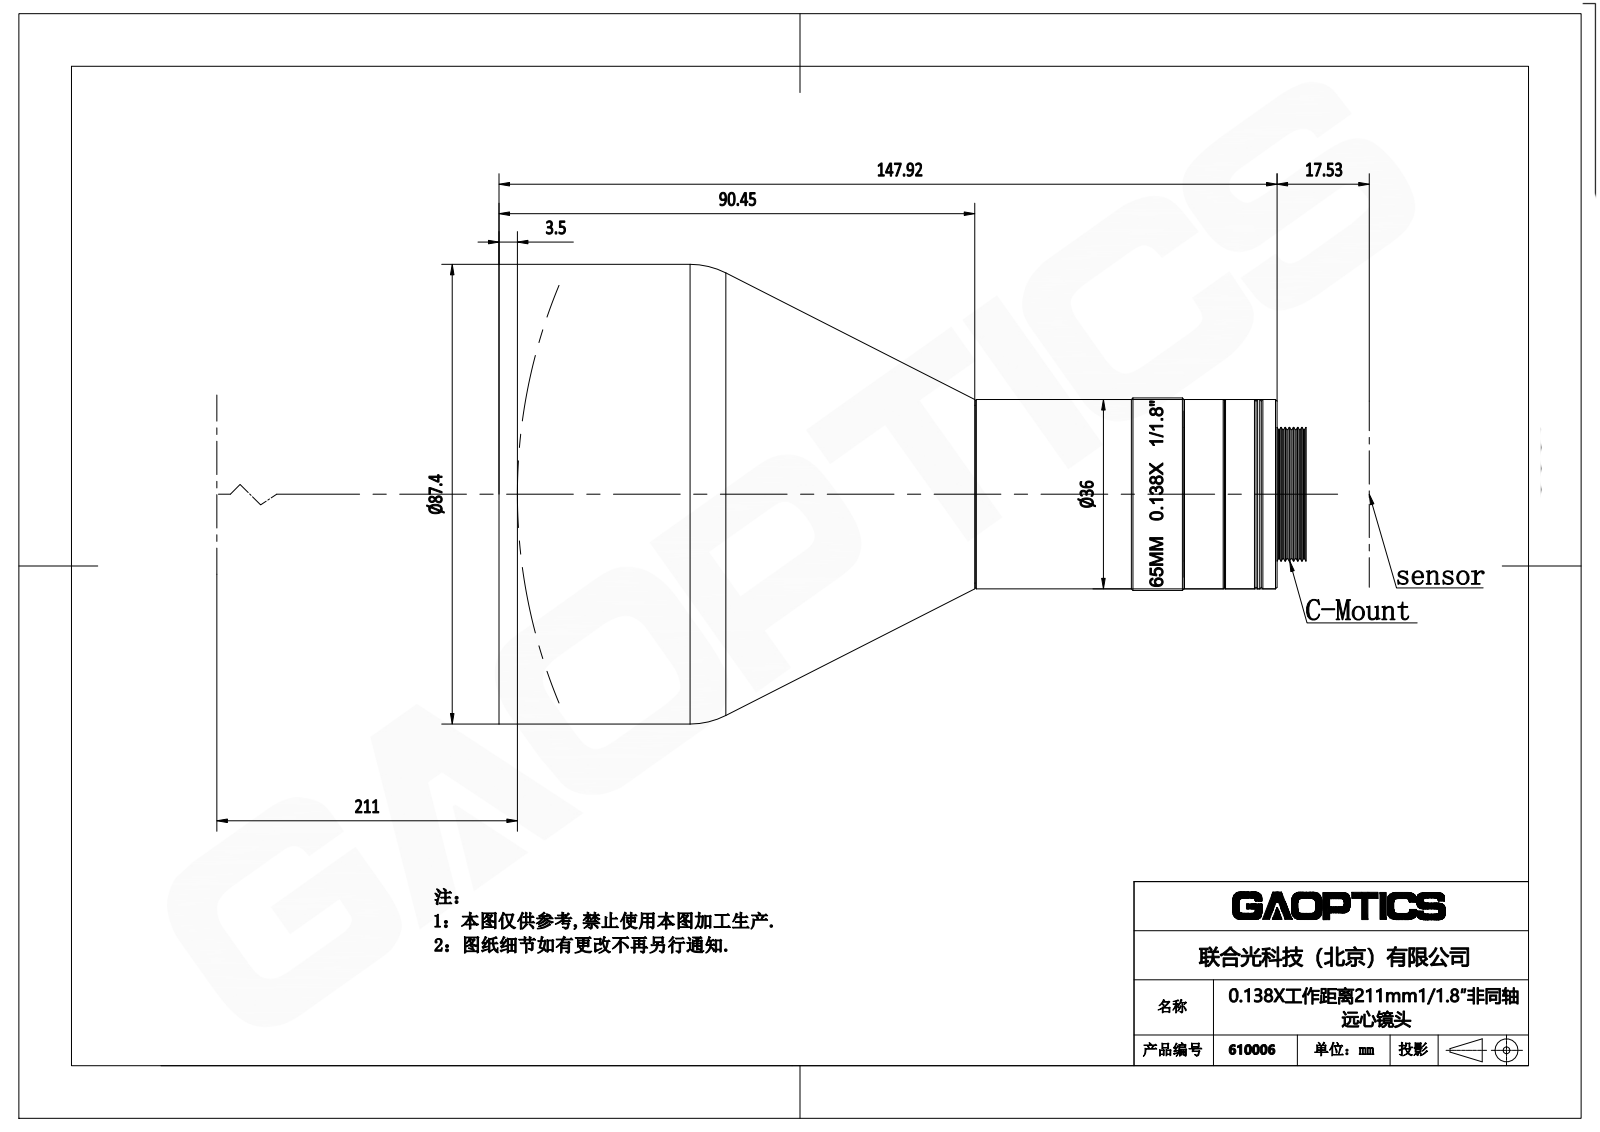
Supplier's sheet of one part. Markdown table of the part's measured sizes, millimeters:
| quantity | value |
| --- | --- |
| part name | 610006 |
| STEP written by | SolidWorks 2016 (AUTOMOTIVE_DESIGN) |
| units | millimeters |
| bodies | 0 solids, 453 faces (100 planar, 113 cylindrical, 240 other) |
| overall size | 153.23 × 87.4 × 87.4 |
| round holes (diameter × count) | 2.2 × 3, 3 × 3, 13.21 × 1, 17.2 × 1, 18.2 × 1, 19.2 × 1, 21.9 × 1, 24.6 × 1, 25.8 × 1, 33 × 1, 35 × 1, 76.4 × 1 |
| round bosses / shafts (diameter × count) | 87.4 × 1, 82 × 1, 36.6 × 1, 36 × 1, 31.6 × 1, 25.4 × 1, 24.54 × 1, 24.3 × 1 |
| partial cylindrical surfaces (radius × count) | 0.5 × 2, 18.2 × 1 |
| main face-to-face distances | 6, 3, 47.23, 54.28, 7.05, 137.24, 53.28, 6.05, 1, 90.46 |
| hole center spacings | 14.5, 25.12 |
